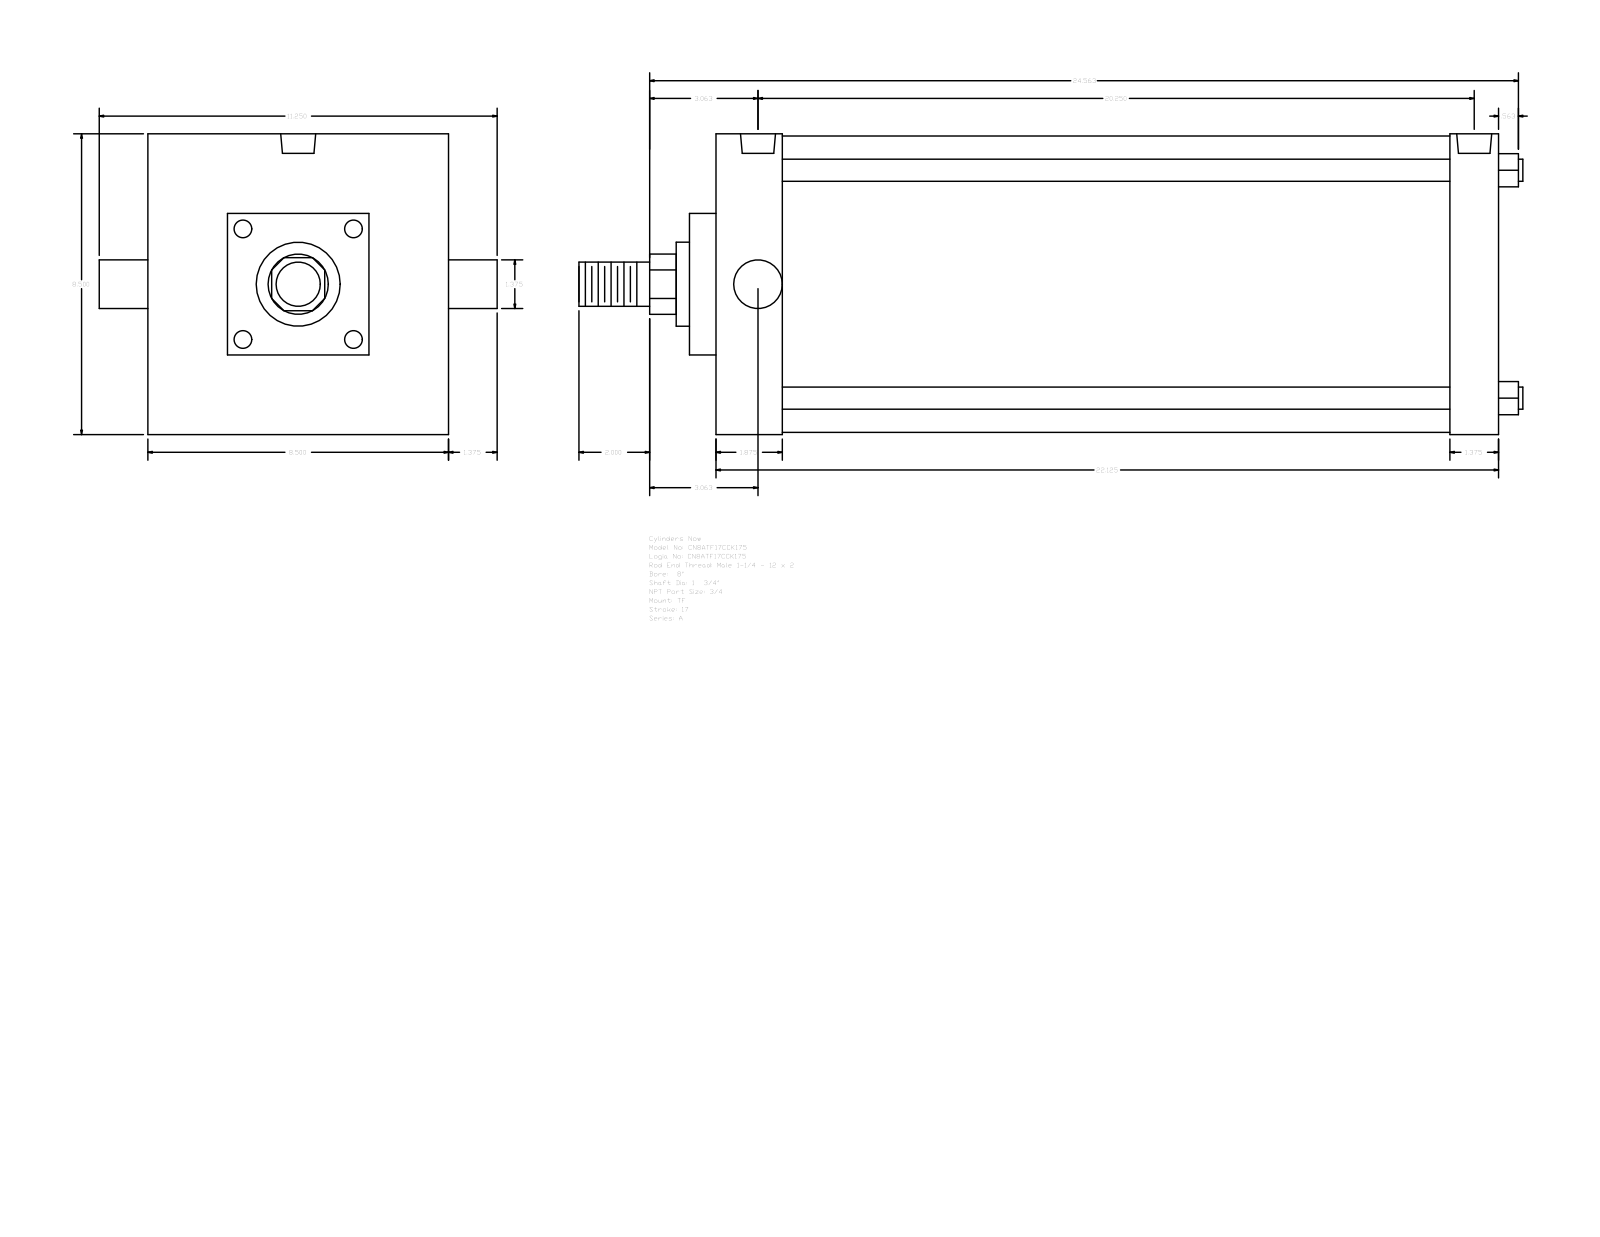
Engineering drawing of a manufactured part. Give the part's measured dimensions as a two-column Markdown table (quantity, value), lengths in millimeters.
| quantity | value |
| --- | --- |
| part name | A_TF__0800_1.75 |
| STEP written by | GSSL Pune (CONFIG_CONTROL_DESIGN) |
| units | millimeters |
| bodies | 0 solids, 89 faces (65 planar, 24 cylindrical, 0 other) |
| overall size | 677.86 × 285.75 × 215.9 |
| round holes (diameter × count) | 15.08 × 3, 25.12 × 2 |
| round bosses / shafts (diameter × count) | 15.88 × 4, 212.72 × 1, 60.33 × 1, 44.45 × 1, 34.92 × 1, 31.75 × 1 |
| partial cylindrical surfaces (radius × count) | 21.63 × 1 |
| main face-to-face distances | 561.98, 215.9, 34.93, 47.63, 514.35, 527.05, 479.42, 19.05, 57.15, 158.75 |
| hole center spacings | 6.35, 508, 501.65, 514.35 |
